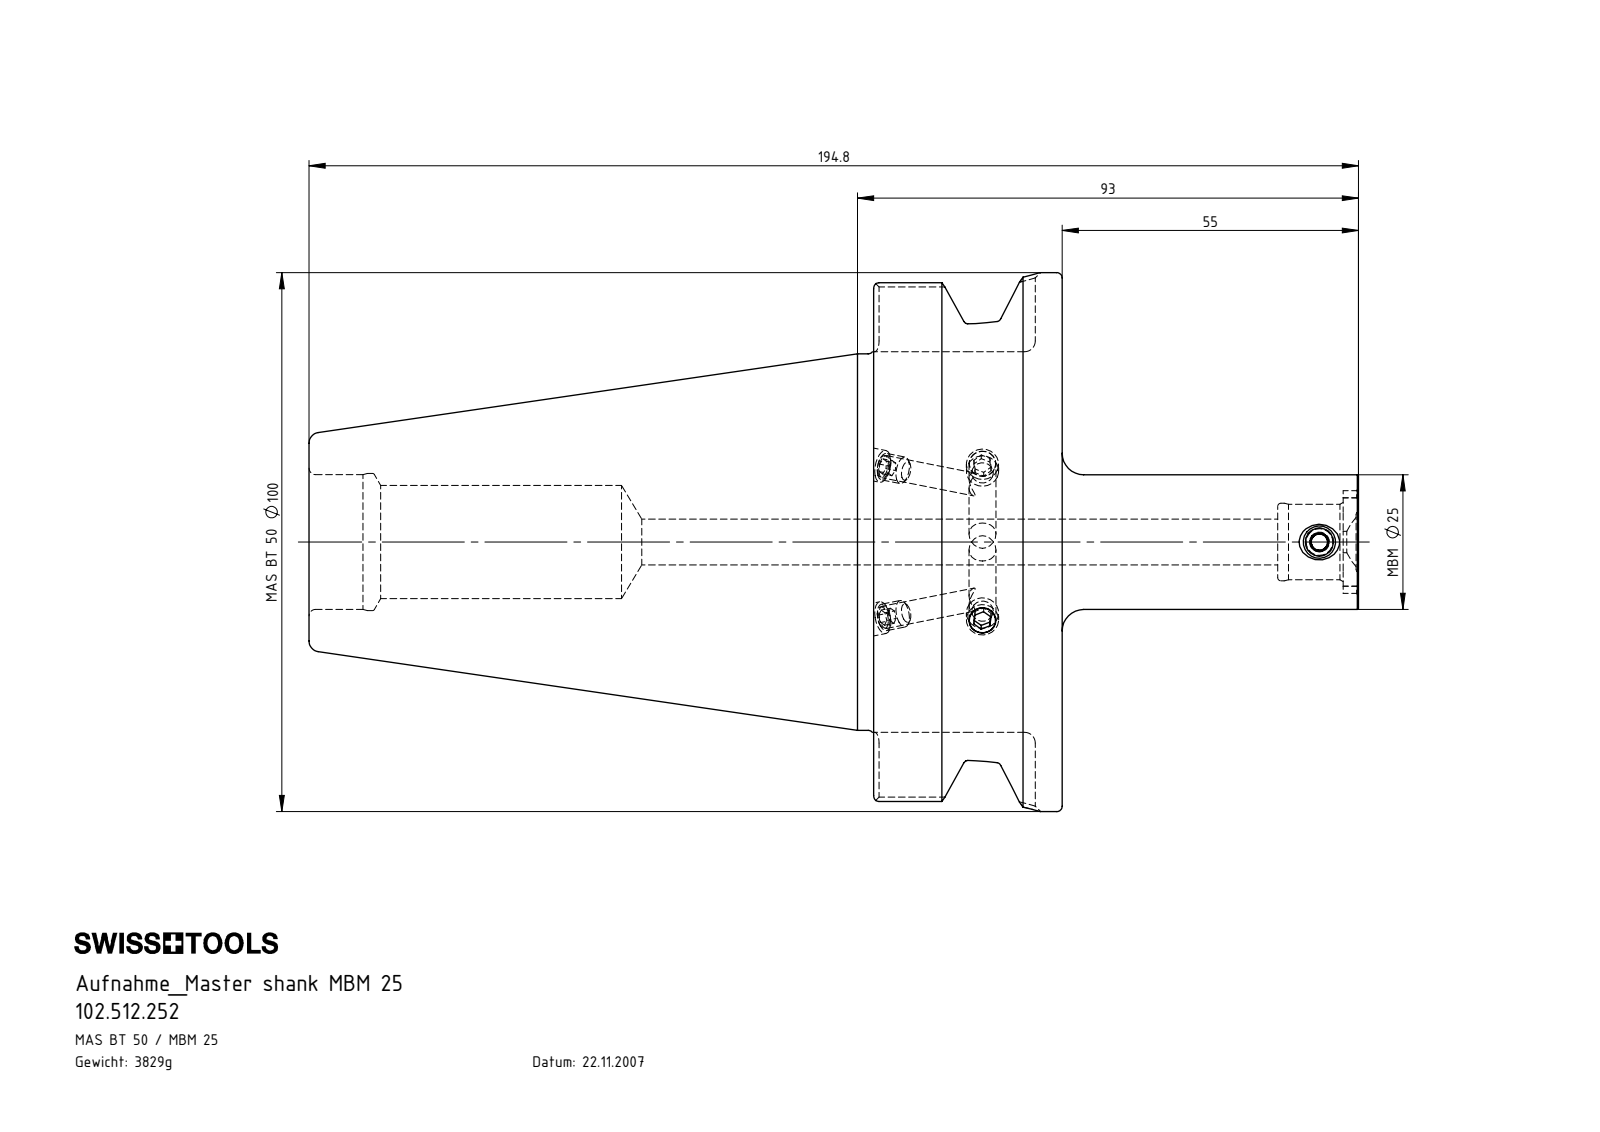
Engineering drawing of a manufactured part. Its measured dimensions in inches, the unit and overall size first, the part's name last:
Units: inches
Overall size (bounding box): 7.669 × 3.937 × 3.937
Round holes (diameter × count): ⌀0.165 ×2, ⌀0.236 ×2, ⌀0.197 ×1, ⌀0.207 ×1, ⌀0.335 ×1, ⌀0.551 ×1, ⌀0.567 ×1, ⌀0.827 ×1, ⌀0.984 ×1, ⌀1.002 ×1
Round bosses / shafts (diameter × count): ⌀3.937 ×1, ⌀3.346 ×1, ⌀2.75 ×1
Partial cylindrical surfaces — rounded edges, fillets, slot ends (radius × count): R0.079 ×8, R0.106 ×4, R0.315 ×1, R0.375 ×1, R0.506 ×1
Main face-to-face distances: 1.378, 2.78, 4.126, 5.504, 1.012, 7.669, 3.543, 2.165, 7.557, 3.431
Volume: 29.75 in³ · Surface area: 89.8 in²
Bodies: 1 solid, 144 faces (27 planar, 58 cylindrical, 59 other)
Part name (STEP PRODUCT): 102.512.252
STEP written by: SolidWorks 2017 (CONFIG_CONTROL_DESIGN)
